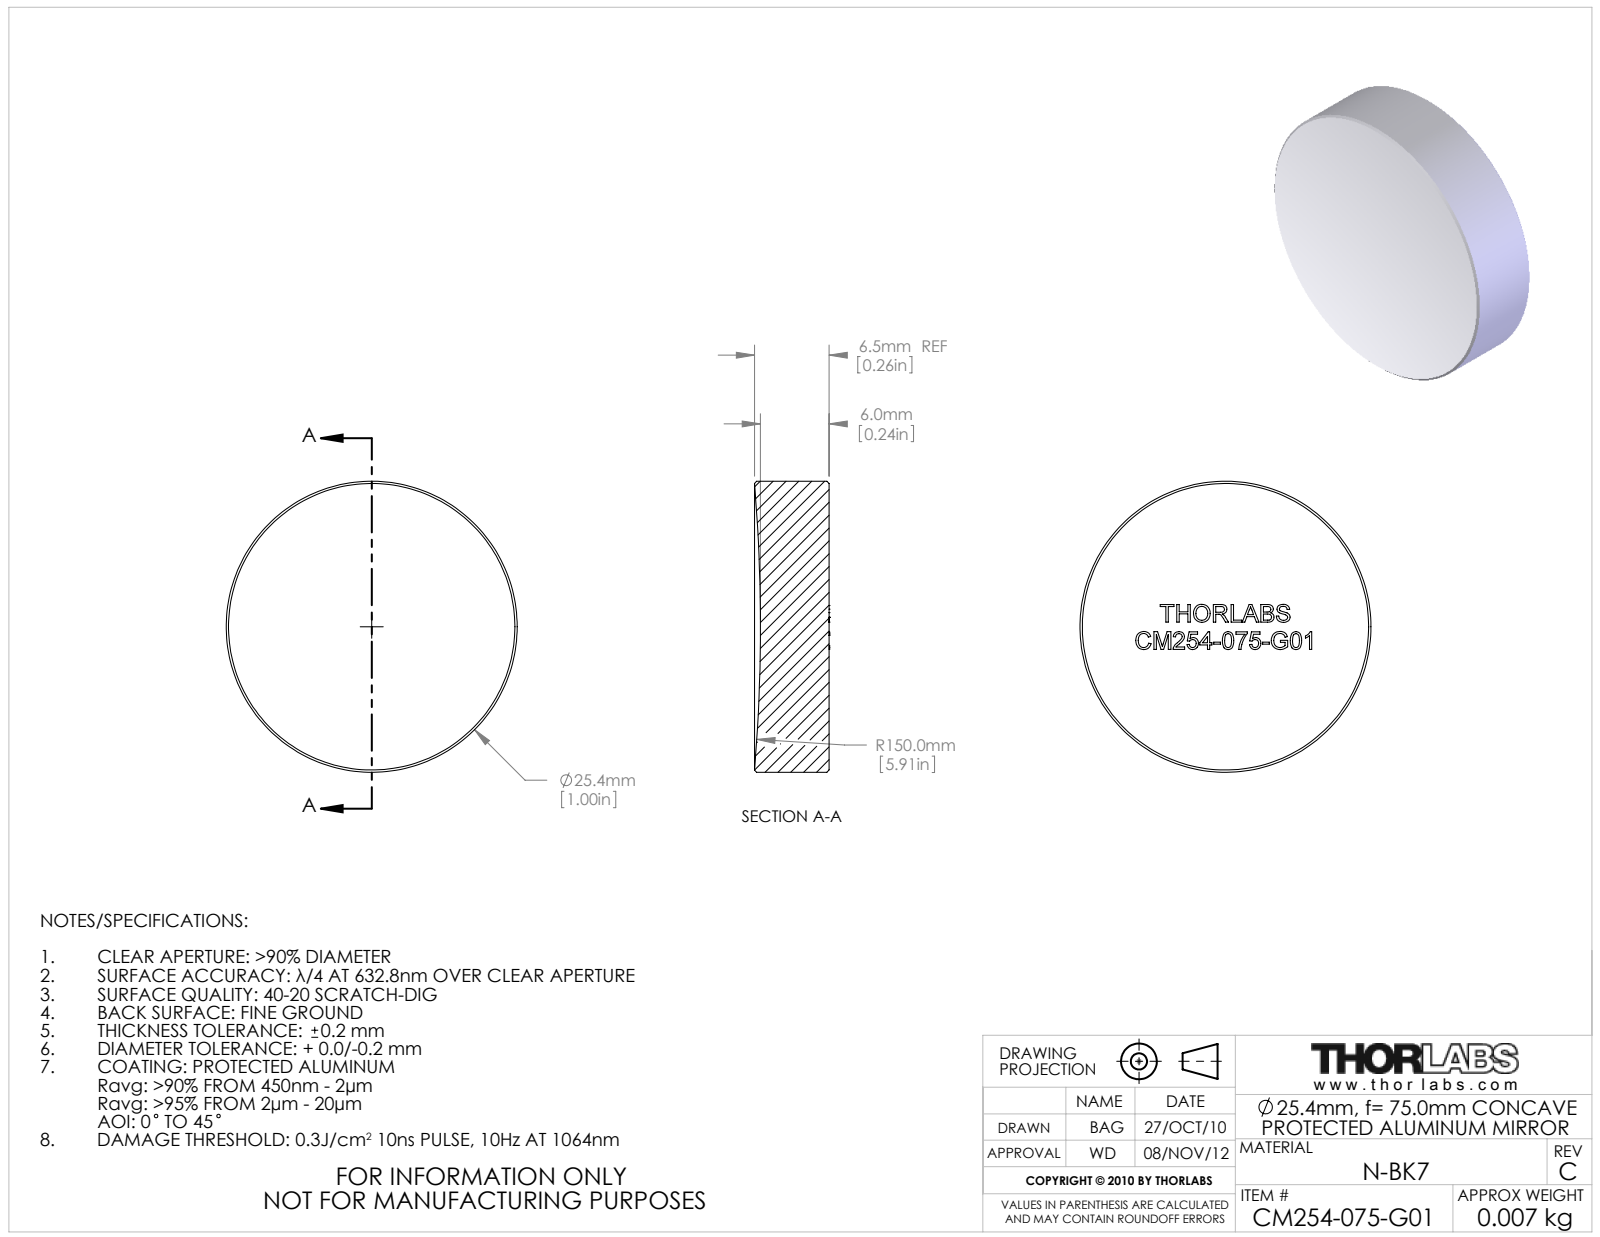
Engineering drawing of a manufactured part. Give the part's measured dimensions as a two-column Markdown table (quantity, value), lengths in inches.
| quantity | value |
| --- | --- |
| part name | 12011-E0W |
| STEP written by | SolidWorks 2009 (AUTOMOTIVE_DESIGN) |
| units | inches |
| bodies | 1 solid, 281 faces (160 planar, 2 cylindrical, 119 other) |
| overall size | 1 × 1 × 0.257 |
| volume | 0.194 in³ |
| surface area | 2.35 in² |
| round bosses / shafts (diameter × count) | 1 × 1 |
| main face-to-face distances | 0.076, 0.061, 0.029, 0.067, 0.094, 0.163, 0.052, 0.037, 0.155, 0.087 |
